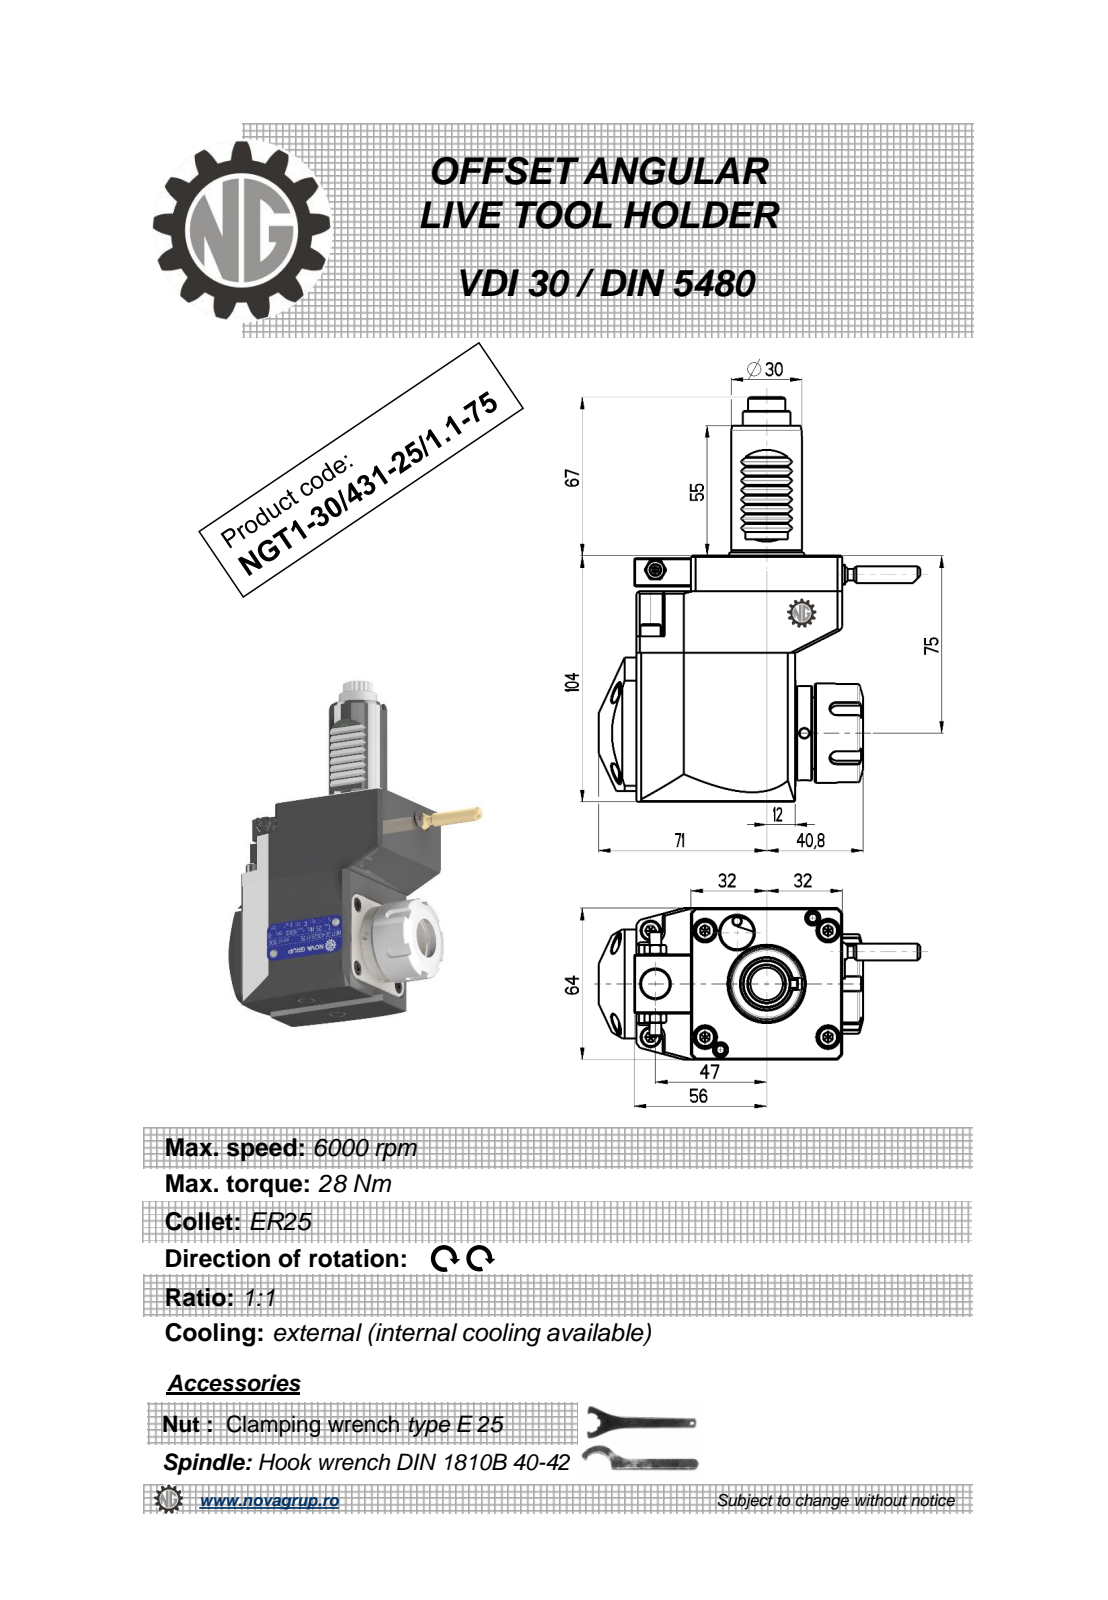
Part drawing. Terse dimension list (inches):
name: NGT1_30_431_25_1_1_75
written by: PRO/ENGINEER BY PARAMETRIC TECHNOLOGY CORPORATION, 2010280 (CONFIG_CONTROL_DESIGN)
unit: in
bodies: 1 solid, 538 faces (216 planar, 161 cylindrical, 161 other)
size: 6.732 × 5.35 × 2.575
volume: 34.41 in³; area: 85 in²
holes: 2× ⌀0.157, 1× ⌀0.098, 1× ⌀0.118, 1× ⌀0.165, 1× ⌀0.374, 1× ⌀0.472, 1× ⌀0.799
bosses: 2× ⌀0.353, 2× ⌀0.197, 1× ⌀1.654, 1× ⌀1.575, 1× ⌀1.299, 1× ⌀1.181, 1× ⌀0.787, 1× ⌀0.276
rounds: 36× R0.078, 12× R0.01, 8× R0.012, 5× R0.118, 4× R0.138, 2× R0.157, 1× R0.279, 1× R0.312
face distances: 2.52, 4.094, 3.425, 0.591, 0.78, 0.787, 2.646, 3.504, 2.638, 0.039
hole spacings: 0.533, 2.478, 2.677, 2.691, 3.677
